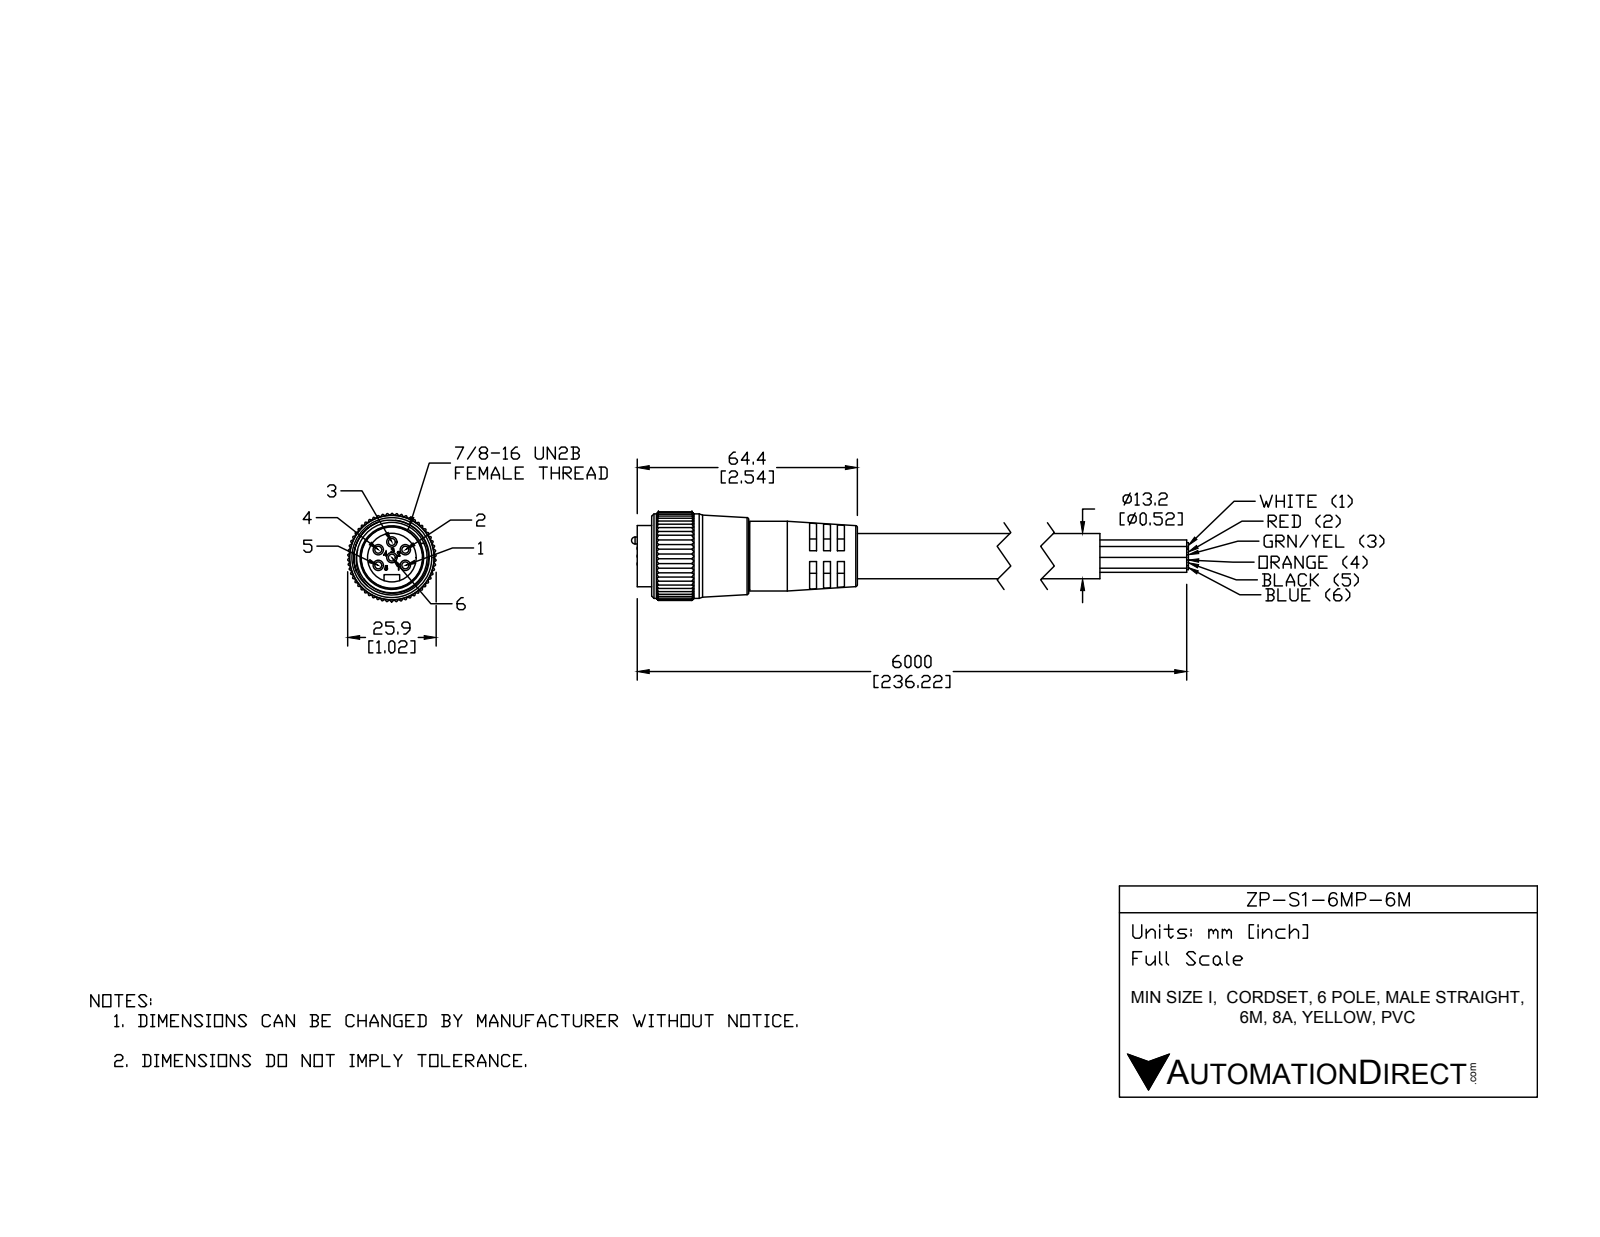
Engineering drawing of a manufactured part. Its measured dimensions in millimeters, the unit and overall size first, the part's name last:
Units: millimetres
Overall size (bounding box): 111.28 × 52.91 × 25.84
Round holes (diameter × count): ⌀14.22 ×1, ⌀19.96 ×1, ⌀20.45 ×1, ⌀21 ×1
Round bosses / shafts (diameter × count): ⌀3.05 ×6, ⌀2 ×6, ⌀13.21 ×2, ⌀24.68 ×1, ⌀20.4 ×1, ⌀19.5 ×1, ⌀17.88 ×1
Partial cylindrical surfaces — rounded edges, fillets, slot ends (radius × count): R0.25 ×165, R2.29 ×1, R5.25 ×1, R12.93 ×1
Main face-to-face distances: 2, 4.04, 2.04, 6.04, 2.02, 8.06, 6.06, 4.02, 4.03, 10.07
Volume: 31 376 mm³ · Surface area: 13 508 mm²
Bodies: 8 solids, 638 faces (229 planar, 326 cylindrical, 83 other)
Part name (STEP PRODUCT): ZP-S1-6MP-6M
STEP written by: SolidWorks 2015 (AUTOMOTIVE_DESIGN)
